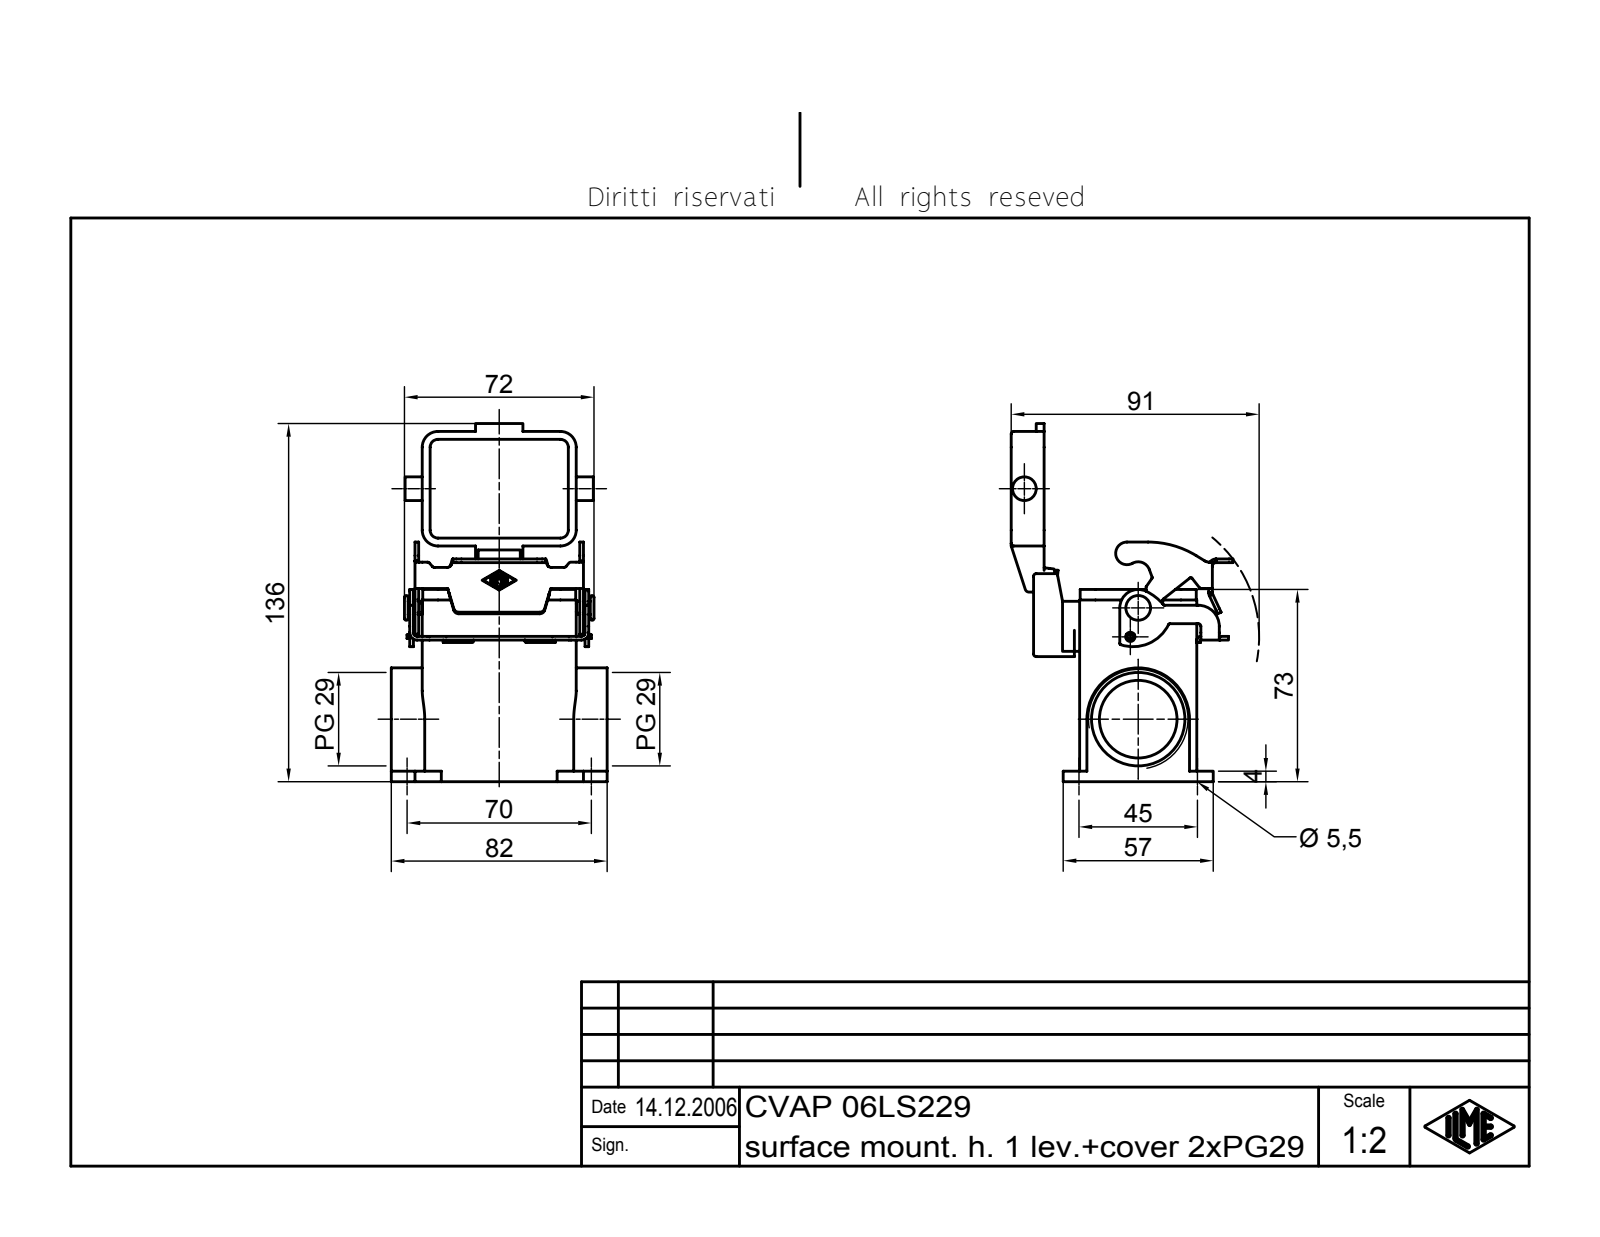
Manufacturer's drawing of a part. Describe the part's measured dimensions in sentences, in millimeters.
The part is named "CVAP 06LS229". Its 3-D file was written by "Autodesk Inventor 7 (AUTOMOTIVE_DESIGN)". It is 4 solids with 574 faces: 222 planar, 187 cylindrical and 165 other. Overall it measures 136 by 84.23 by 82 millimeters. Its volume is 111 781 cubic millimeters and its surface area 62 561 square millimeters. Round holes: 4 of diameter 5.5, 1 of diameter 3.5, 1 of diameter 4, 1 of diameter 29.48, 1 of diameter 35.48. Round bosses or shafts: 2 of diameter 5, 1 of diameter 9, 1 of diameter 7, 1 of diameter 3.2, 1 of diameter 3. Partial cylindrical surfaces (rounded edges, fillets, slot ends): 27 of radius 1, 15 of radius 0.25, 10 of radius 0.5, 10 of radius 1.5, 8 of radius 6, 7 of radius 2, 6 of radius 1.4, 6 of radius 2.8. The main face-to-face distances are 4, 40.5, 44.5, 26, 30, 36.5, 70.5, 66.5, 2.5, 68. The hole center spacings are 45, 70, 83.22, 31.4.
